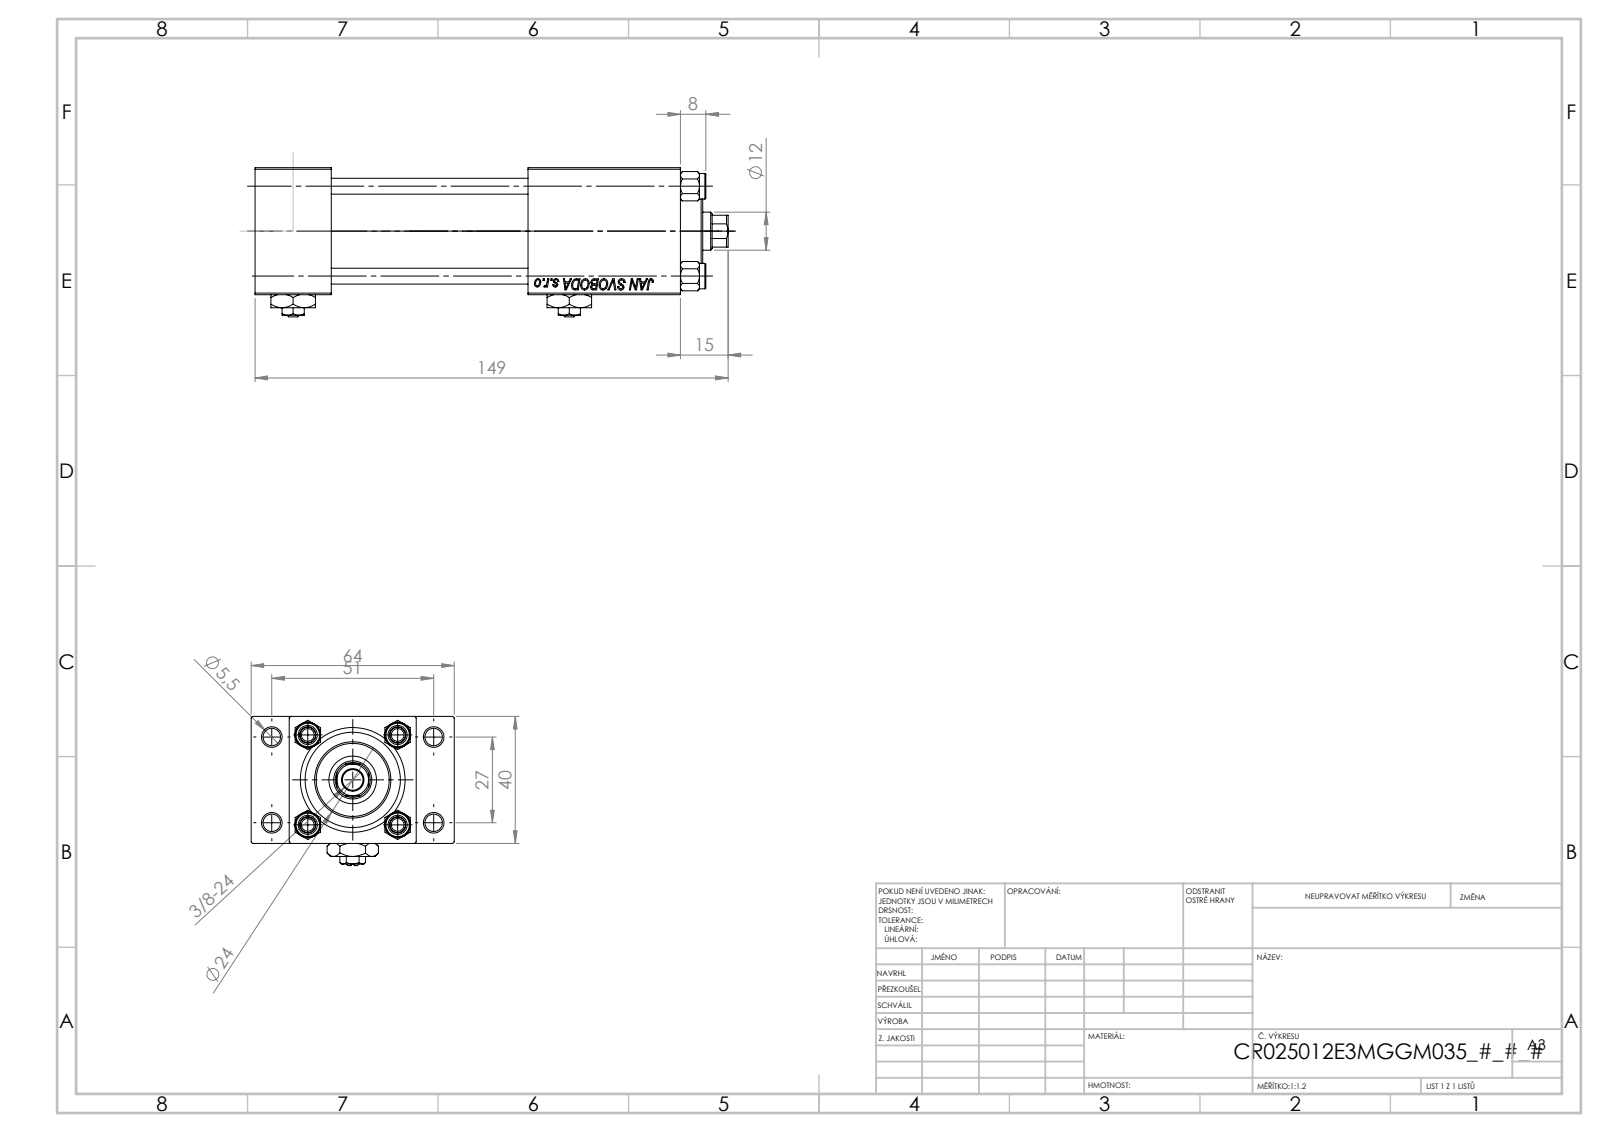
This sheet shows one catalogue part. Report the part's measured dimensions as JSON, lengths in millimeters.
{"part_name": "V215CR_VCP_E; Zatka_pro_OIL_PORT; V215CR_TYCINKA_E; V215CR_E_Body (+2 more)", "step_written_by": "SolidWorks 2019 (CONFIG_CONTROL_DESIGN)", "units": "millimeters", "bodies": {"solids": 13, "faces": 1236, "planar": 544, "cylindrical": 98, "other": 594}, "overall_size": [149, 64, 47], "volume_mm3": 169022, "surface_area_mm2": 68083, "round_holes": [[5, 4], [5.5, 4], [20, 3], [7, 2], [13.16, 2], [6.5, 1], [12, 1], [15, 1], [25, 1], [30, 1]], "round_bosses_or_shafts": [[8, 4], [31, 1], [24, 1]], "partial_cylinders_radius": [[5.5, 1]], "face_to_face_distances": [40, 24, 12, 52, 39.8, 134, 110, 105.3, 81.3, 28.7], "hole_center_spacings": [11.37, 20.01, 28.3, 28.85, 29.89, 39.66, 48.34, 27]}
